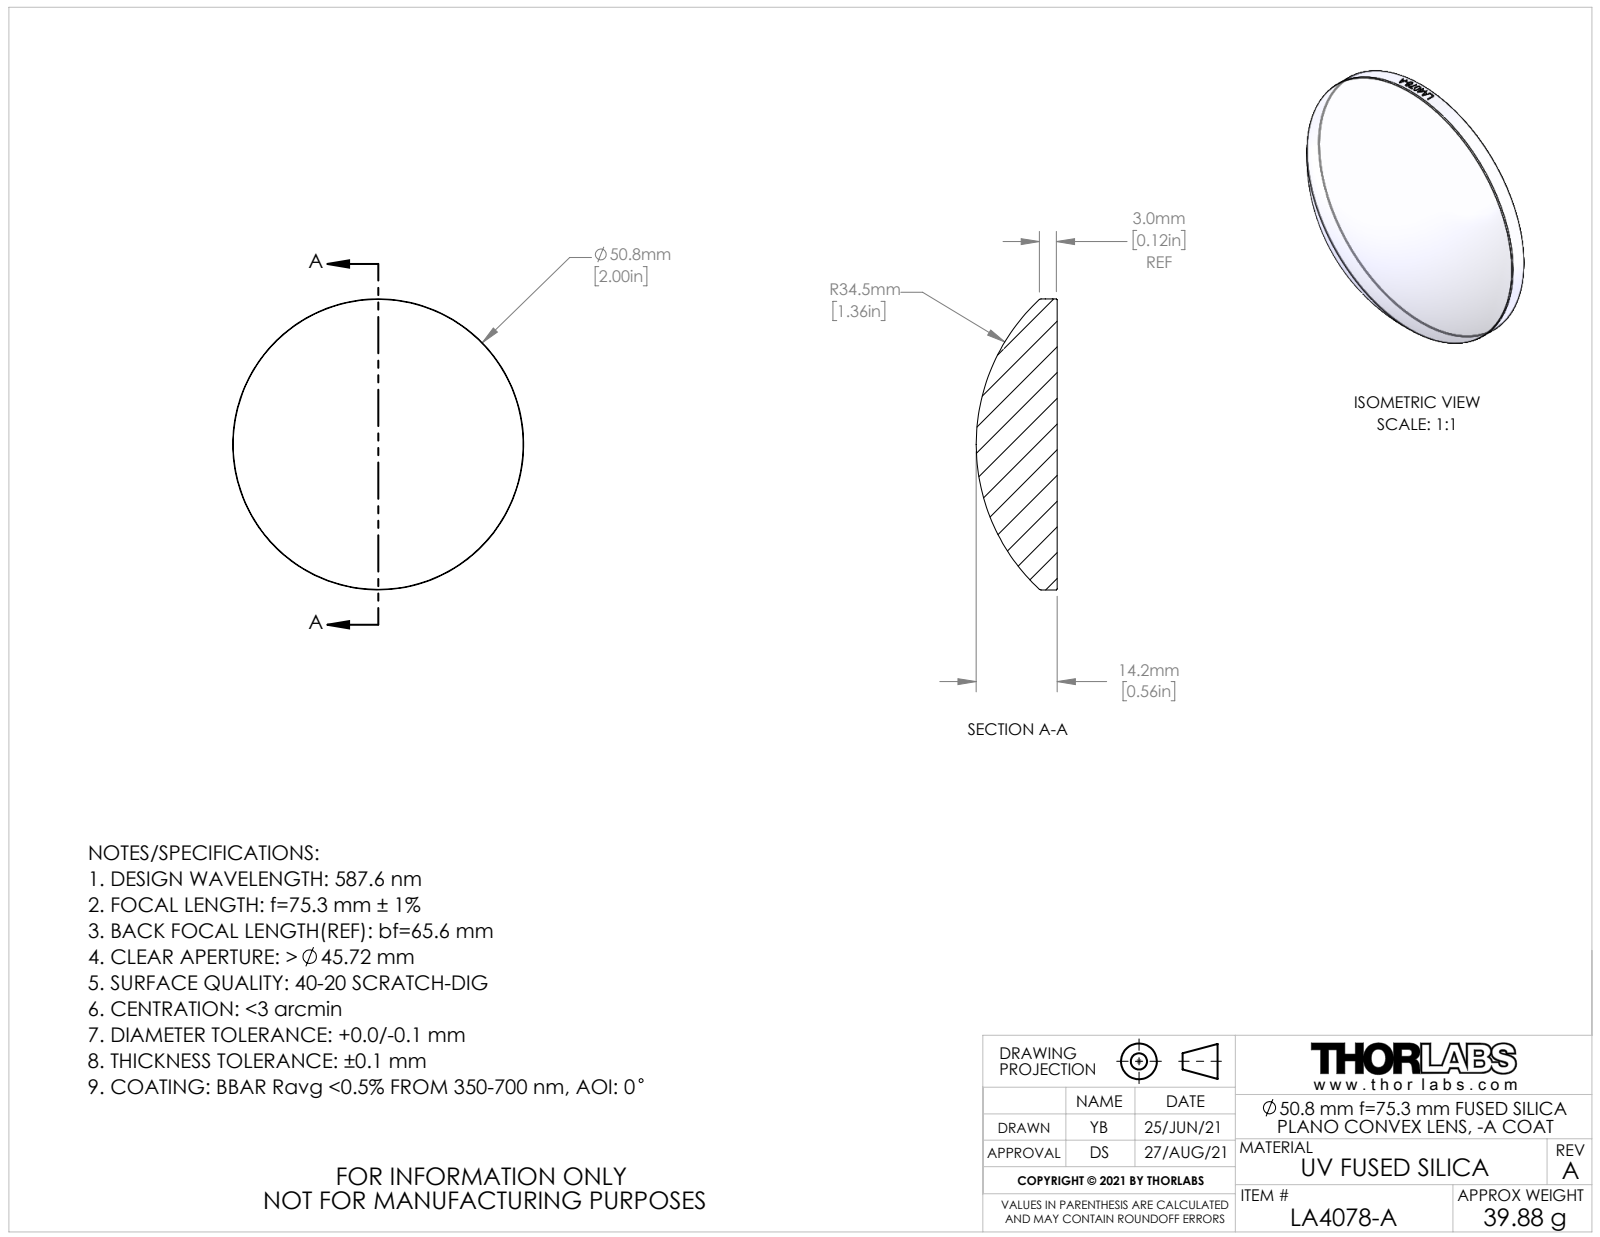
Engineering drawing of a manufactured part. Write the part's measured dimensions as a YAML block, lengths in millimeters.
part_name: "CTN017536-E0W; CTN017564"
step_written_by: "SolidWorks 2018 (AUTOMOTIVE_DESIGN)"
units: millimeters
bodies: {solids: 1, faces: 23, planar: 1, cylindrical: 16, other: 6}
overall_size: [50.8, 50.8, 14.15]
volume: 18102
surface_area: 4906
round_bosses_or_shafts:
  - {diameter: 50.8, count: 1}
